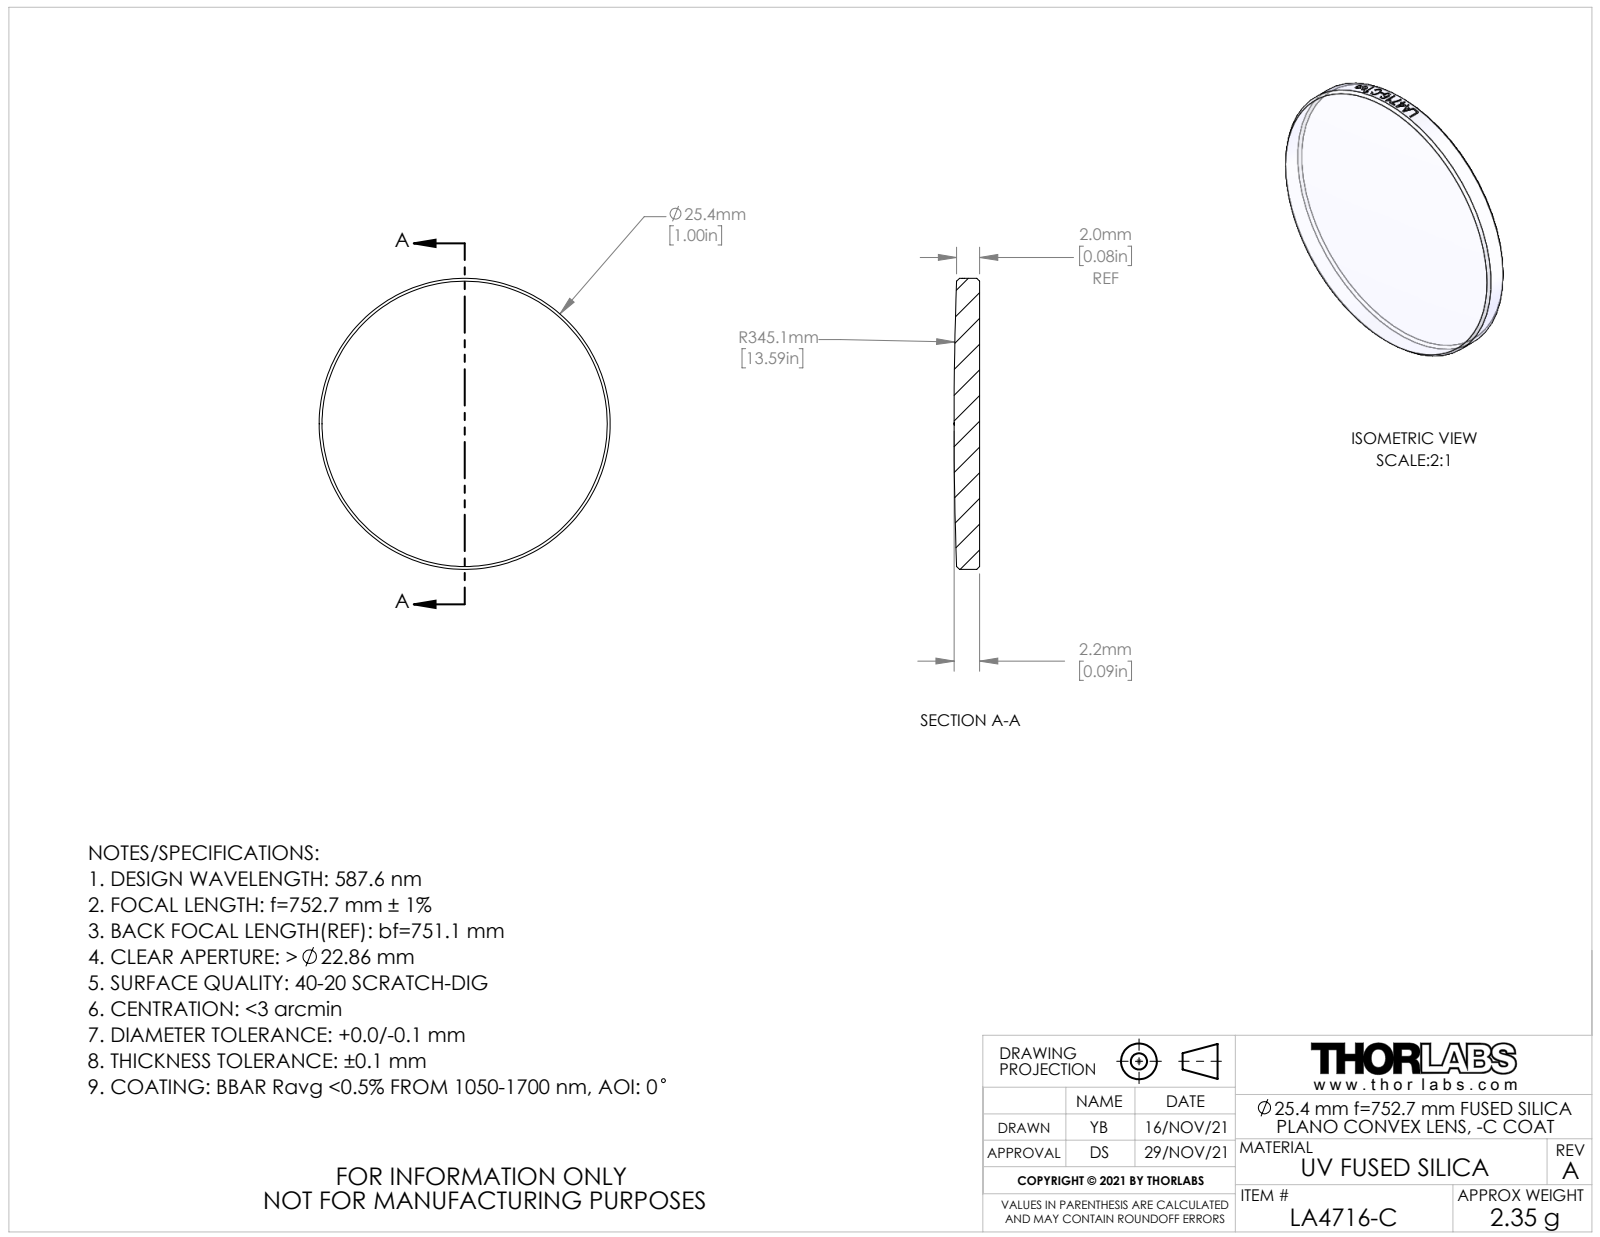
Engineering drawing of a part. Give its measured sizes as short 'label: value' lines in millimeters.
name: CTN018139; CTN018070-E0W
written by: SolidWorks 2018 (AUTOMOTIVE_DESIGN)
unit: mm
bodies: 1 solid, 24 faces (1 planar, 17 cylindrical, 6 other)
size: 25.4 × 25.4 × 2.23
volume: 1 067 mm³; area: 1 150 mm²
bosses: 1× ⌀25.4
